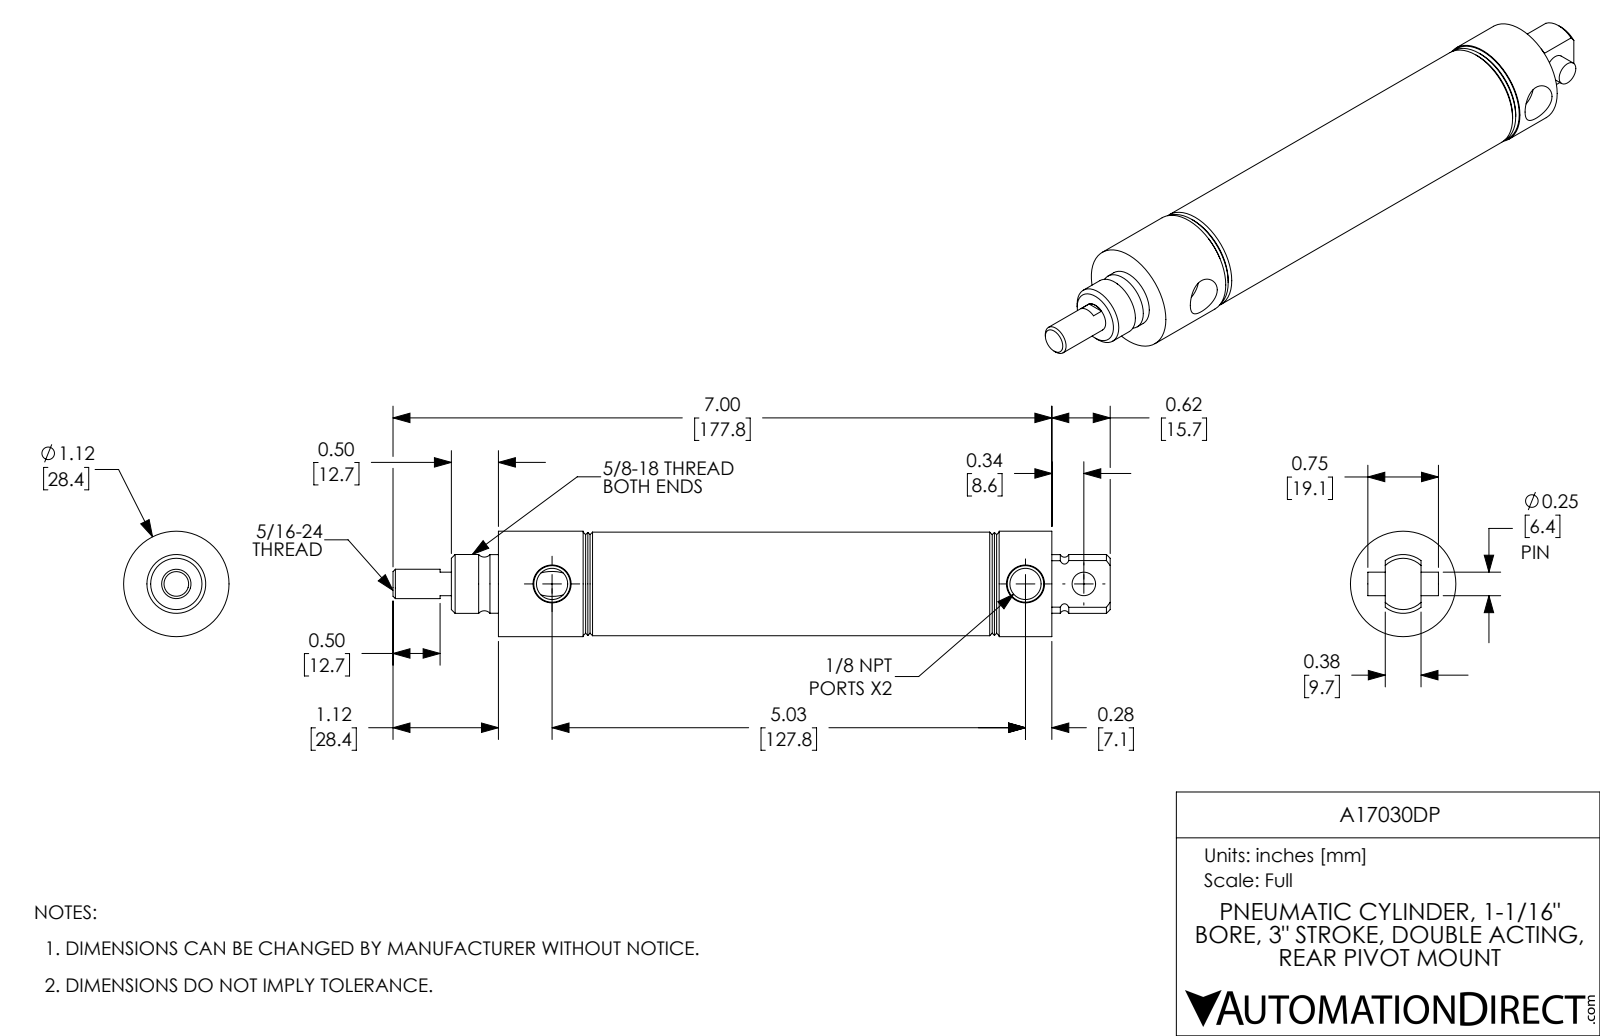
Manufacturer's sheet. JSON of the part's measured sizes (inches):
{"part_name": "A17030DP; A17030DP-PIN; A17030DP-Rod; A17030DP-MainBody", "step_written_by": "SolidWorks 2017 (AUTOMOTIVE_DESIGN)", "units": "inches", "bodies": {"solids": 3, "faces": 91, "planar": 23, "cylindrical": 30, "other": 38}, "overall_size": [7.62, 1.12, 1.12], "volume_in3": 3.448, "surface_area_in2": 50.09, "round_holes": [[0.332, 2], [0.25, 1], [0.312, 1], [1.063, 1]], "round_bosses_or_shafts": [[1.12, 1], [1.1, 1], [0.625, 1], [0.623, 1]], "partial_cylinders_radius": [[0.313, 1]], "face_to_face_distances": [0.5, 4.69, 3.5, 3, 1.19, 1.69, 4.69, 5.88, 4.19, 1.19], "hole_center_spacings": [0.62, 5.03, 5.65]}
